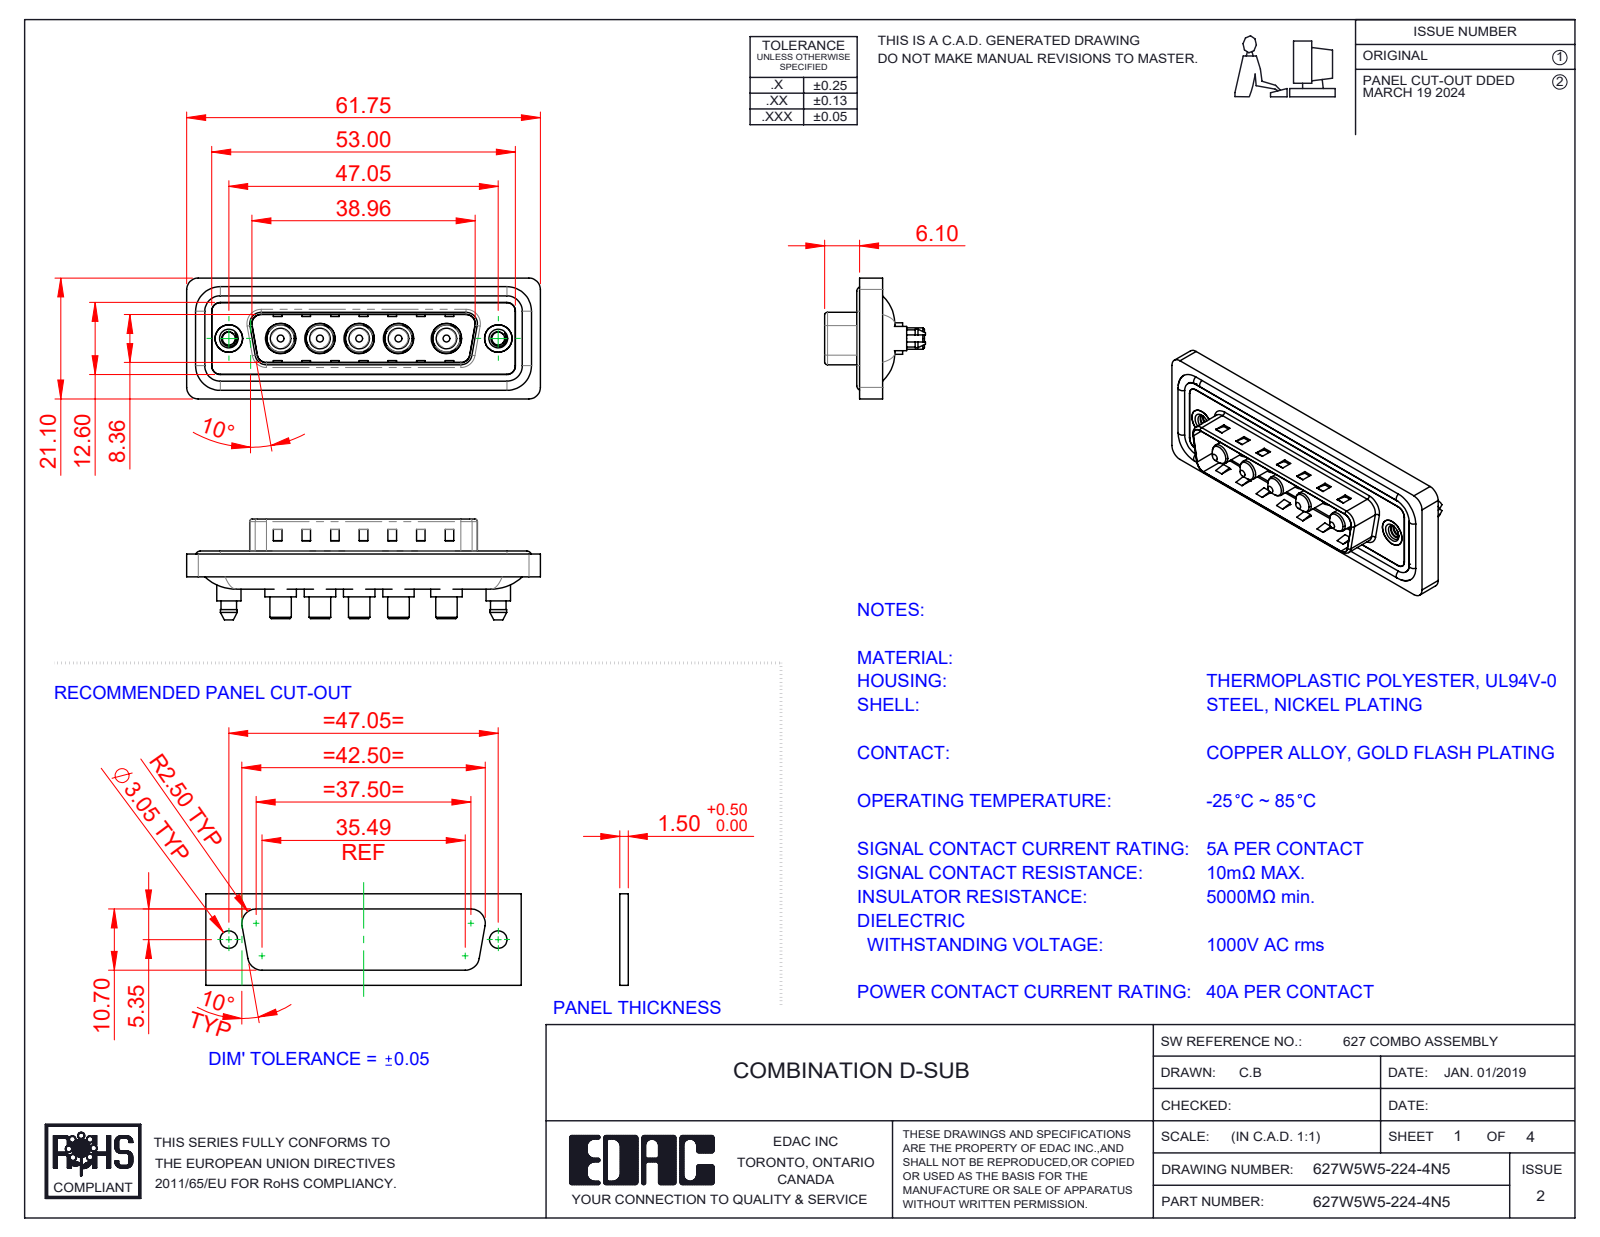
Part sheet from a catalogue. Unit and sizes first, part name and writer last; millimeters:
Units: millimetres
Overall size (bounding box): 61.75 × 21.1 × 17.6
Round holes (diameter × count): ⌀4.85 ×5, ⌀5.3 ×5, ⌀2.26 ×2, ⌀4 ×2, ⌀4.8 ×2, ⌀5 ×2
Round bosses / shafts (diameter × count): ⌀5.5 ×5, ⌀5.2 ×5, ⌀4.75 ×5, ⌀3.75 ×5, ⌀3.6 ×5, ⌀1.6 ×4, ⌀5.4 ×2, ⌀4.9 ×2
Partial cylindrical surfaces — rounded edges, fillets, slot ends (radius × count): R1.5 ×24, R2 ×18, R1.6 ×10, R0.5 ×8, R2.1 ×5, R0.25 ×4, R0.6 ×4, R0.65 ×4
Main face-to-face distances: 0.4, 1.5, 3.1, 1.1, 0.5, 1.6, 2.9, 0.82, 9.58, 5.65
Hole centre spacings: 6.86, 9.04, 13.73, 38.01, 6.87, 8.37, 8.38, 9.05
Volume: 7 699 mm³ · Surface area: 12 184 mm²
Bodies: 17 solids, 728 faces (275 planar, 315 cylindrical, 138 other)
Part name (STEP PRODUCT): 627Combo Shell Rear_25 Contacts; Power Pin_40A S; 627W5W5-224-4N5; 627Combo Housing_5W5 (+3 more)
STEP written by: SolidWorks 2023 (CONFIG_CONTROL_DESIGN)
